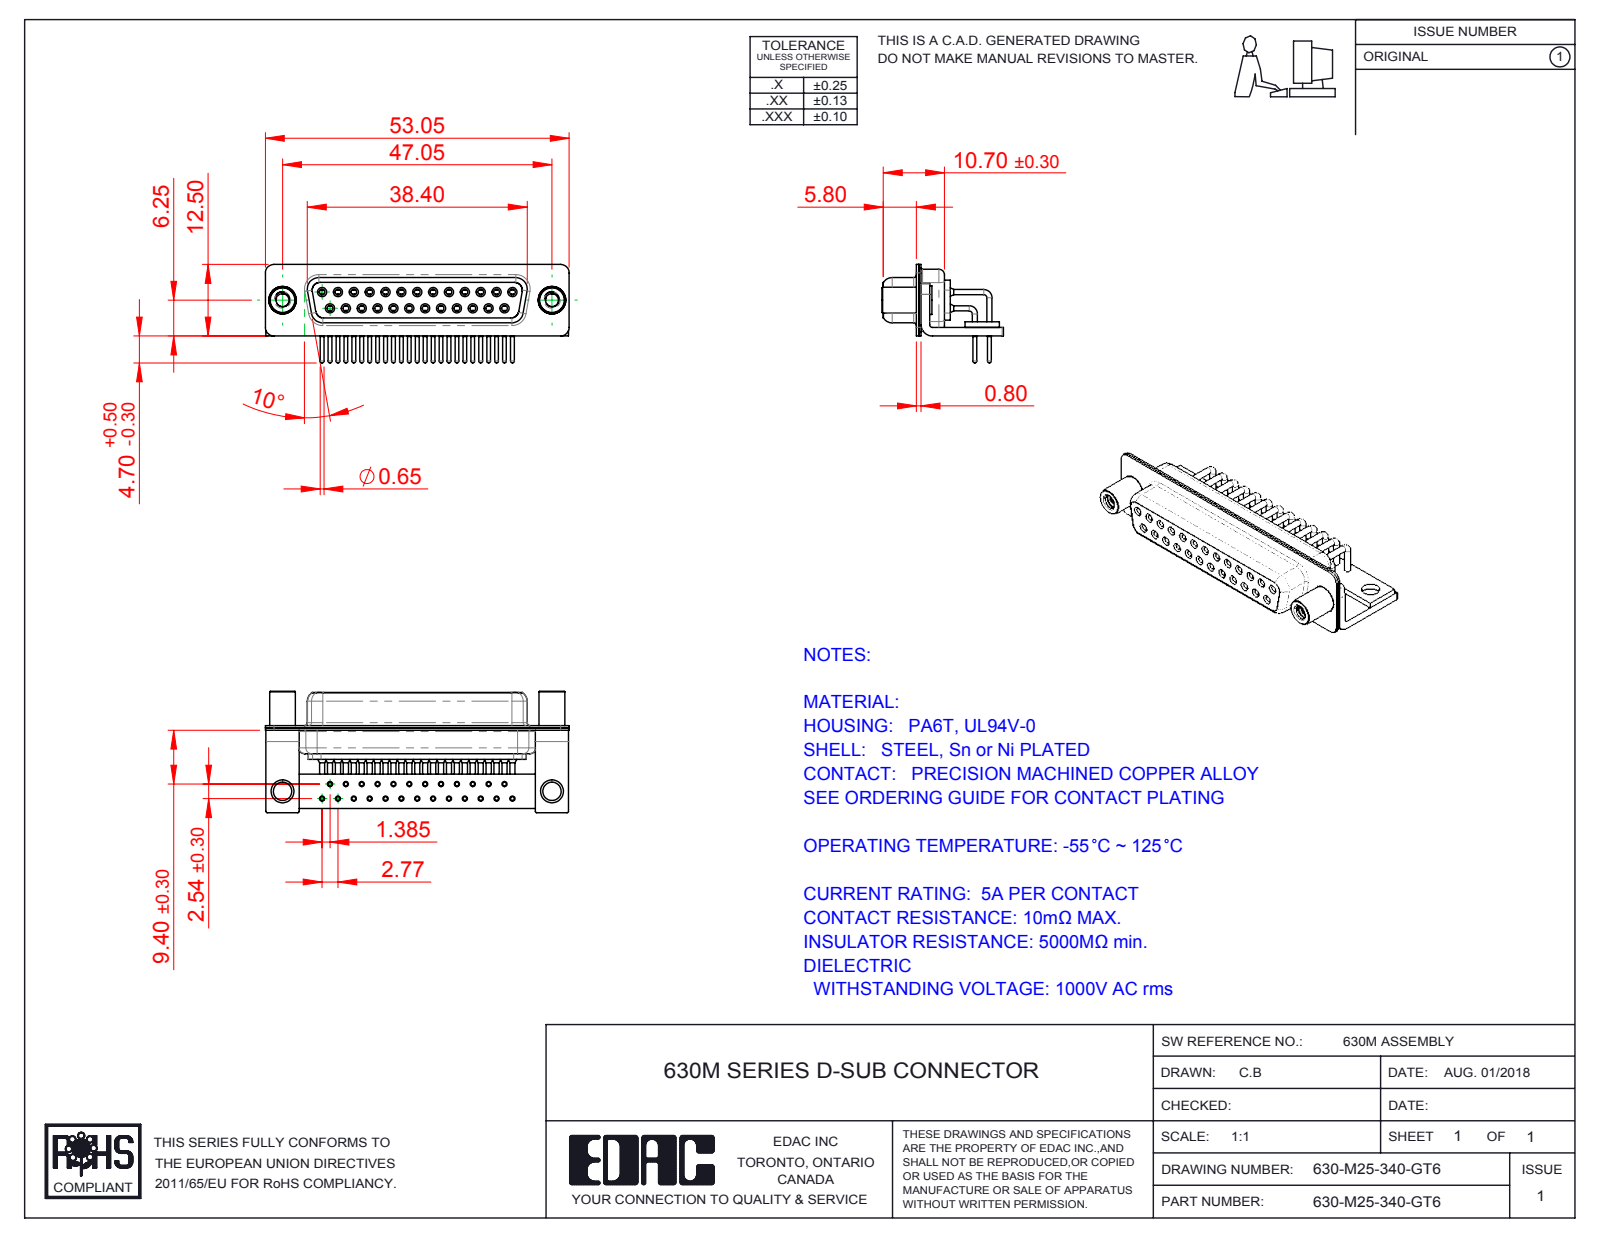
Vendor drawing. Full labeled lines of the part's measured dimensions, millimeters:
Part name (STEP PRODUCT): 630M Contact Row 1; 630M Stabilizer Board_25 Contacts; 630-M25-340-GT6; 630M Housing_25 Contacts (+5 more)
STEP written by: SolidWorks 2016 (CONFIG_CONTROL_DESIGN)
Units: millimetres
Bodies: 33 solids, 1754 faces (470 planar, 826 cylindrical, 458 other)
Overall size (bounding box): 53.05 × 21.2 × 17.2
Volume: 4 578 mm³ · Surface area: 11 419 mm²
Round holes (diameter × count): ⌀0.9 ×25, ⌀1 ×25, ⌀1.1 ×25, ⌀1.7 ×25, ⌀1.8 ×25, ⌀2 ×25, ⌀2.26 ×2, ⌀3.2 ×2, ⌀4 ×2, ⌀4.8 ×2
Round bosses / shafts (diameter × count): ⌀1.6 ×25, ⌀1.5 ×25, ⌀0.9 ×25, ⌀0.65 ×25, ⌀5 ×2, ⌀4.9 ×2, ⌀4.5 ×2
Partial cylindrical surfaces — rounded edges, fillets, slot ends (radius × count): R0.25 ×16, R1.5 ×16, R2 ×13, R1.35 ×10, R1.6 ×8, R0.5 ×5, R0.6 ×4, R0.65 ×4
Main face-to-face distances: 0.4, 2.3, 1.9, 1.45, 8.95, 0.85, 9.35, 0.8, 6.2, 1
Hole centre spacings: 2.77, 5.54, 8.31, 11.08, 13.85, 3.16, 4.87, 16.62
